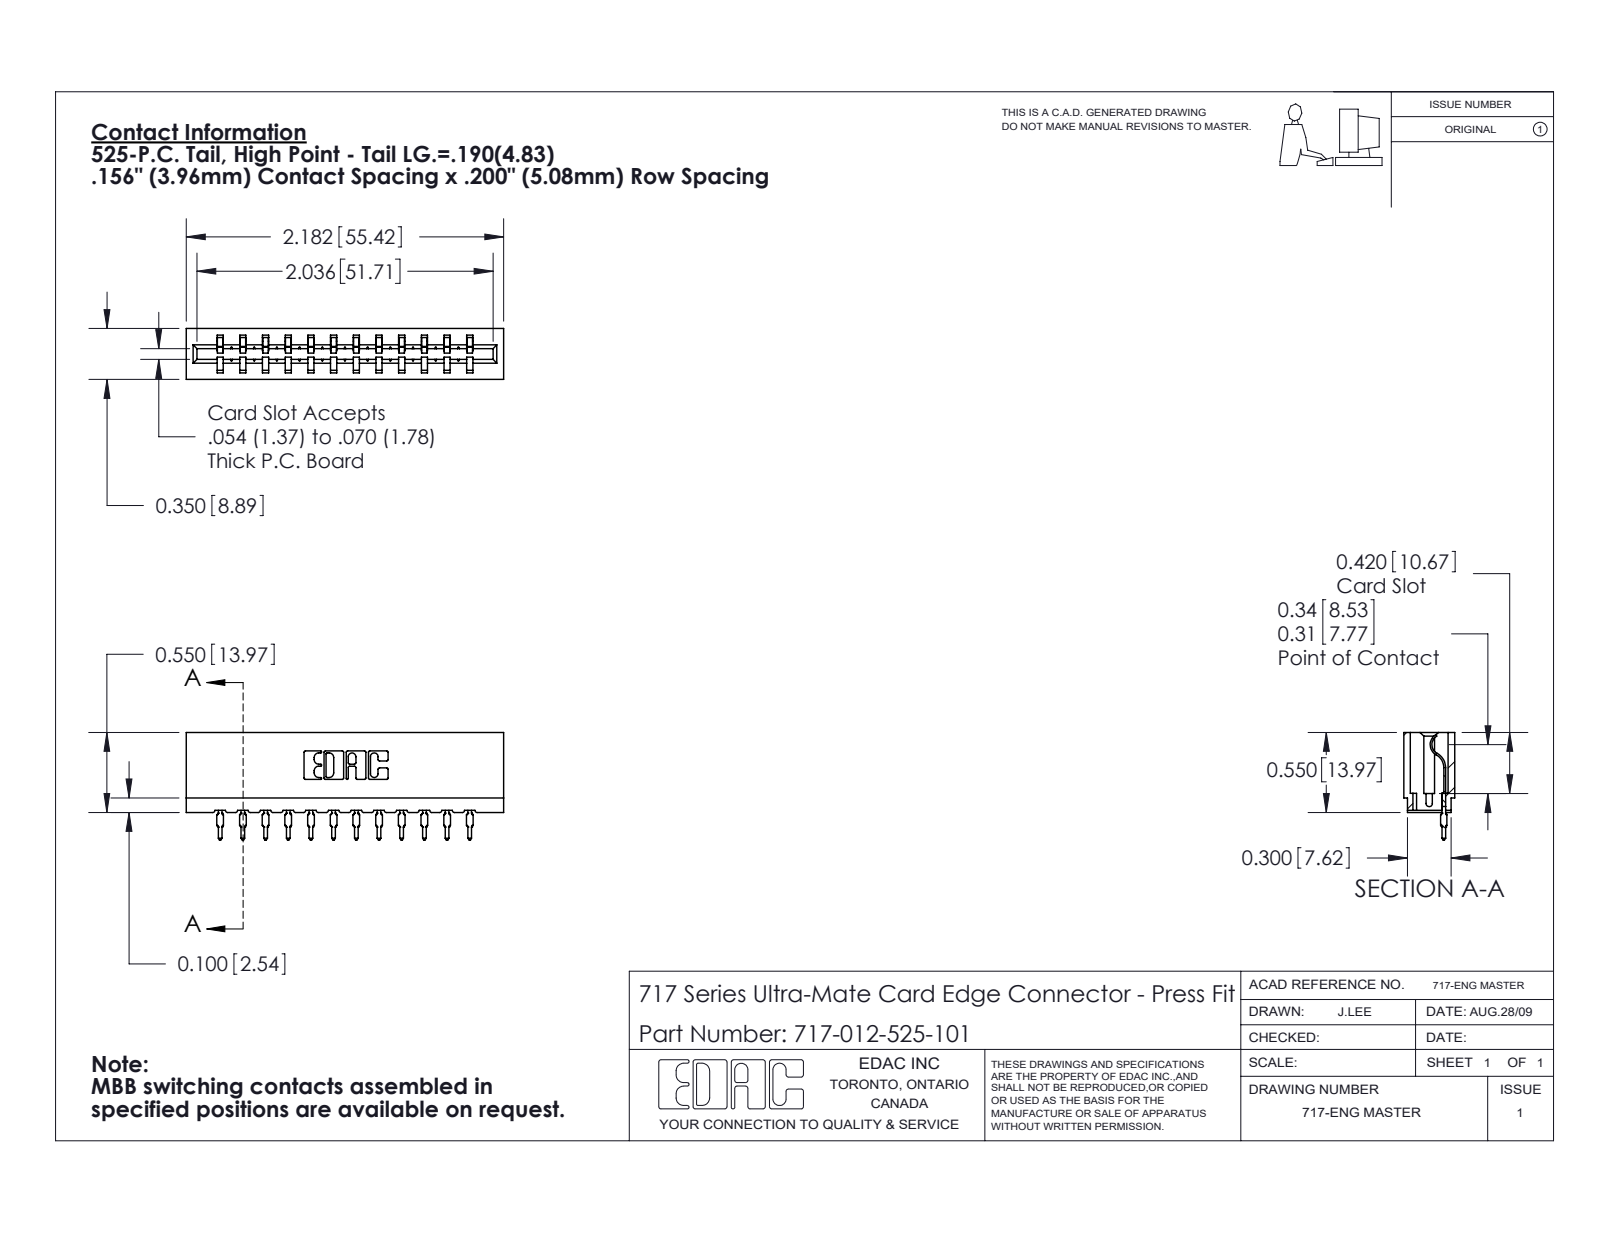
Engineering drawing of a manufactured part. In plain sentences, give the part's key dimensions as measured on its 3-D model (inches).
The part is named "745-292-001_525; 717-012-525-101; 717 Part_Insulator Option - 06". Its 3-D file was written by "SolidWorks 2020 (CONFIG_CONTROL_DESIGN)". It is 13 solids with 1450 faces: 870 planar, 268 cylindrical and 312 other. Overall it measures 2.182 by 0.739 by 0.35 inches. Its volume is 0.293 cubic inches and its surface area 9.902 square inches. Partial cylindrical surfaces (rounded edges, fillets, slot ends): 24 of radius 0.015, 24 of radius 0.021, 22 of radius 0.01, 6 of radius 0.007, 6 of radius 0.031, 4 of radius 0.005, 4 of radius 0.011, 3 of radius 0.026. The main face-to-face distances are 0.212, 0.138, 0.156, 0.624, 0.35, 0.468, 0.198, 0.312, 0.27, 0.312.
